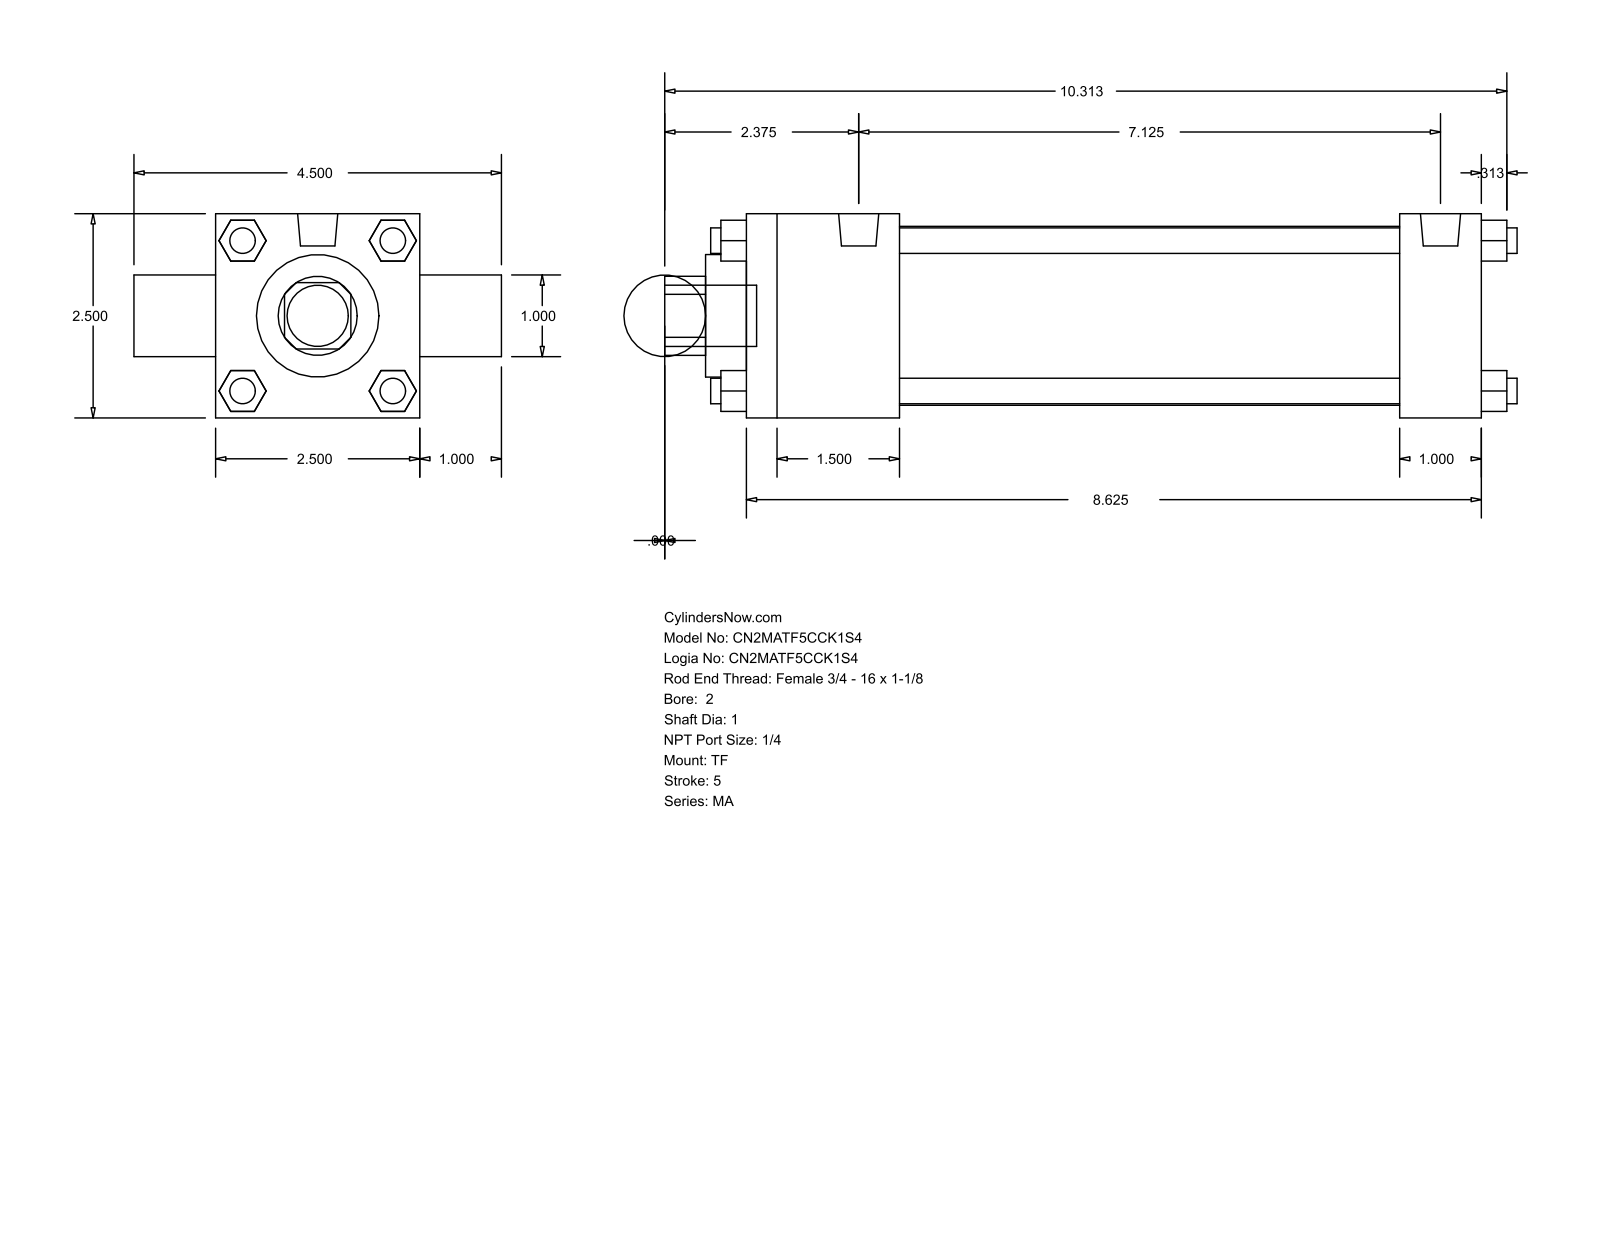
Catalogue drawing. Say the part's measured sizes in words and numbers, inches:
The part is named "MA_TF__0200_1". Its 3-D file was written by "GSSL Pune (CONFIG_CONTROL_DESIGN)". It is 0 solids with 120 faces: 92 planar, 28 cylindrical and 0 other. Overall it measures 10.437 by 4.5 by 2.5 inches. Round holes: 2 of diameter 1, 1 of diameter 1.5, 1 of diameter 2.19. Round bosses or shafts: 7 of diameter 0.313, 2 of diameter 0.492, 1 of diameter 0.75. Partial cylindrical surfaces (rounded edges, fillets, slot ends): 1 of radius 0.484. The main face-to-face distances are 2.5, 1, 9, 0.5, 1.875, 8, 6.125, 7.125, 3.5, 1.593.
